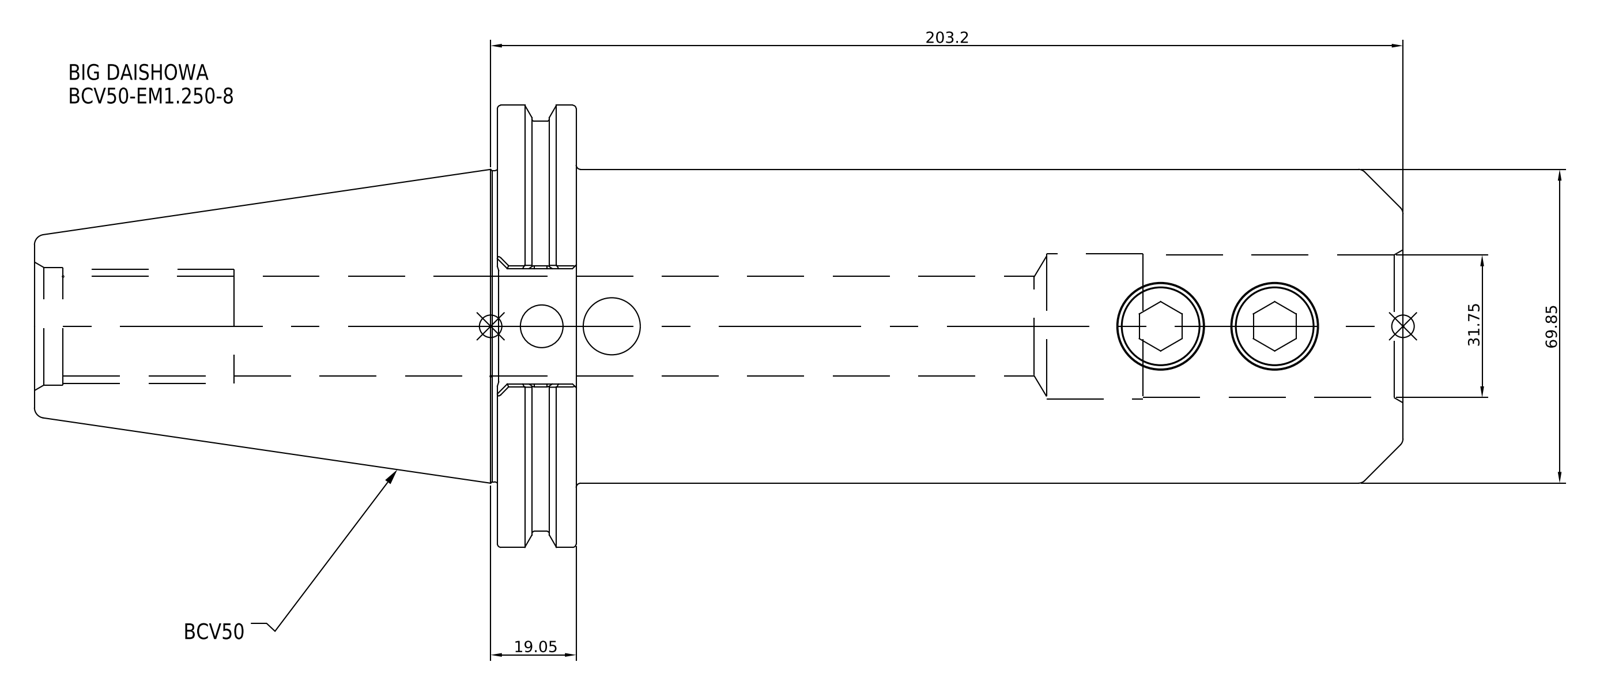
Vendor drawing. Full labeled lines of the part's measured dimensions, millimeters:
Part name (STEP PRODUCT): BCV50-EM1_250-8
STEP written by: SolidWorks 2021 (CONFIG_CONTROL_DESIGN)
Units: millimetres
Bodies: 1 solid, 27 faces (7 planar, 12 cylindrical, 8 other)
Overall size (bounding box): 304.8 × 98.43 × 98.43
Volume: 945 593 mm³ · Surface area: 93 378 mm²
Round holes (diameter × count): ⌀31.75 ×1
Round bosses / shafts (diameter × count): ⌀98.43 ×1, ⌀91.29 ×1, ⌀69.85 ×1
Main face-to-face distances: 17.55, 184.15, 201.7, 304.8, 120.65, 103.1, 168.15, 16, 33.55, 136.65
